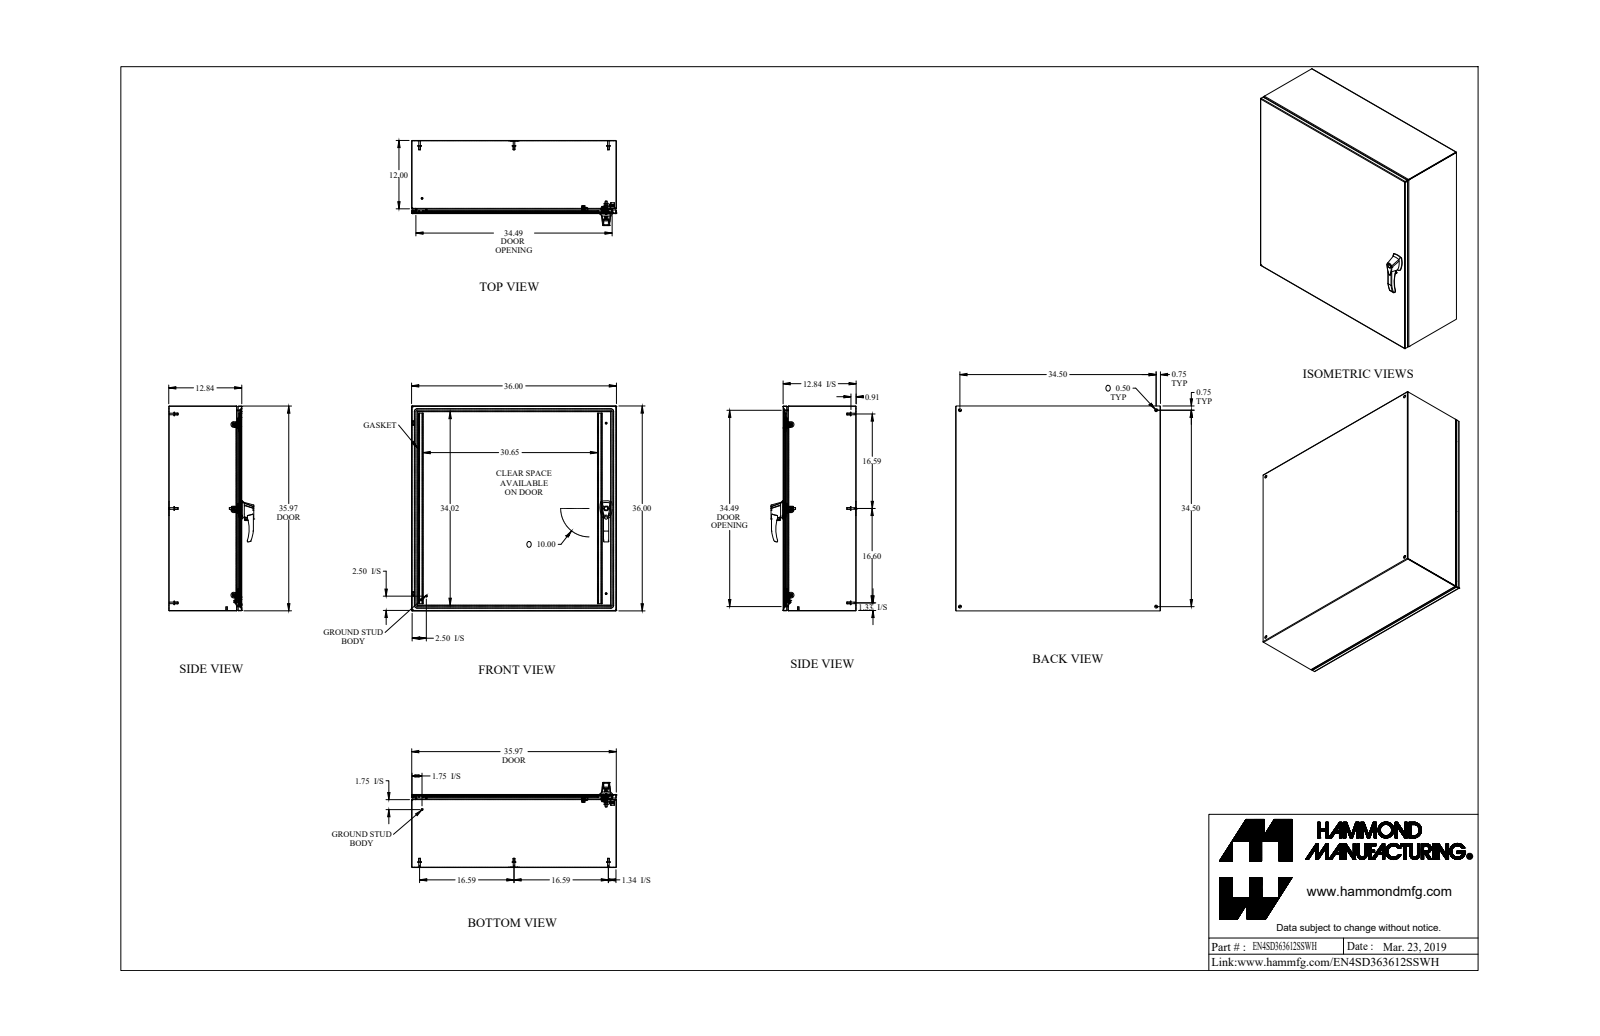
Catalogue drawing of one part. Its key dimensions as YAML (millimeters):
part_name: "EN4SD363612SSWH"
step_written_by: "SolidWorks 2019 (AUTOMOTIVE_DESIGN)"
units: millimeters
bodies: {solids: 64, faces: 1671, planar: 727, cylindrical: 637, other: 307}
overall_size: [914.4, 914.4, 379.9]
volume: 6070000
surface_area: 6550000
round_holes:
  - {diameter: 4.5, count: 6}
  - {diameter: 12.7, count: 4}
  - {diameter: 5, count: 3}
  - {diameter: 6.4, count: 3}
  - {diameter: 6.7, count: 3}
  - {diameter: 8, count: 3}
  - {diameter: 10.5, count: 3}
  - {diameter: 6.5, count: 2}
  - {diameter: 9.5, count: 2}
  - {diameter: 10, count: 2}
  - {diameter: 4.4, count: 1}
  - {diameter: 5.9, count: 1}
round_bosses_or_shafts:
  - {diameter: 8, count: 10}
  - {diameter: 7, count: 8}
  - {diameter: 6.4, count: 7}
  - {diameter: 15.9, count: 6}
  - {diameter: 9.5, count: 6}
  - {diameter: 4, count: 6}
  - {diameter: 25.4, count: 3}
  - {diameter: 15.9, count: 3}
partial_cylinders:
  - {radius: 0.3, count: 24}
  - {radius: 1.2, count: 24}
  - {radius: 0.9, count: 18}
  - {radius: 2.7, count: 18}
  - {radius: 6.4, count: 13}
  - {radius: 1.6, count: 10}
  - {radius: 2.4, count: 10}
  - {radius: 0.4, count: 9}
face_to_face_distances: [1.8, 324.4, 912.6, 322.6, 326.2, 910.7, 914.4, 21.4, 303, 1]
hole_center_spacings: [876.3, 20, 63.6, 380.6, 380.6, 380.6, 381, 439]
